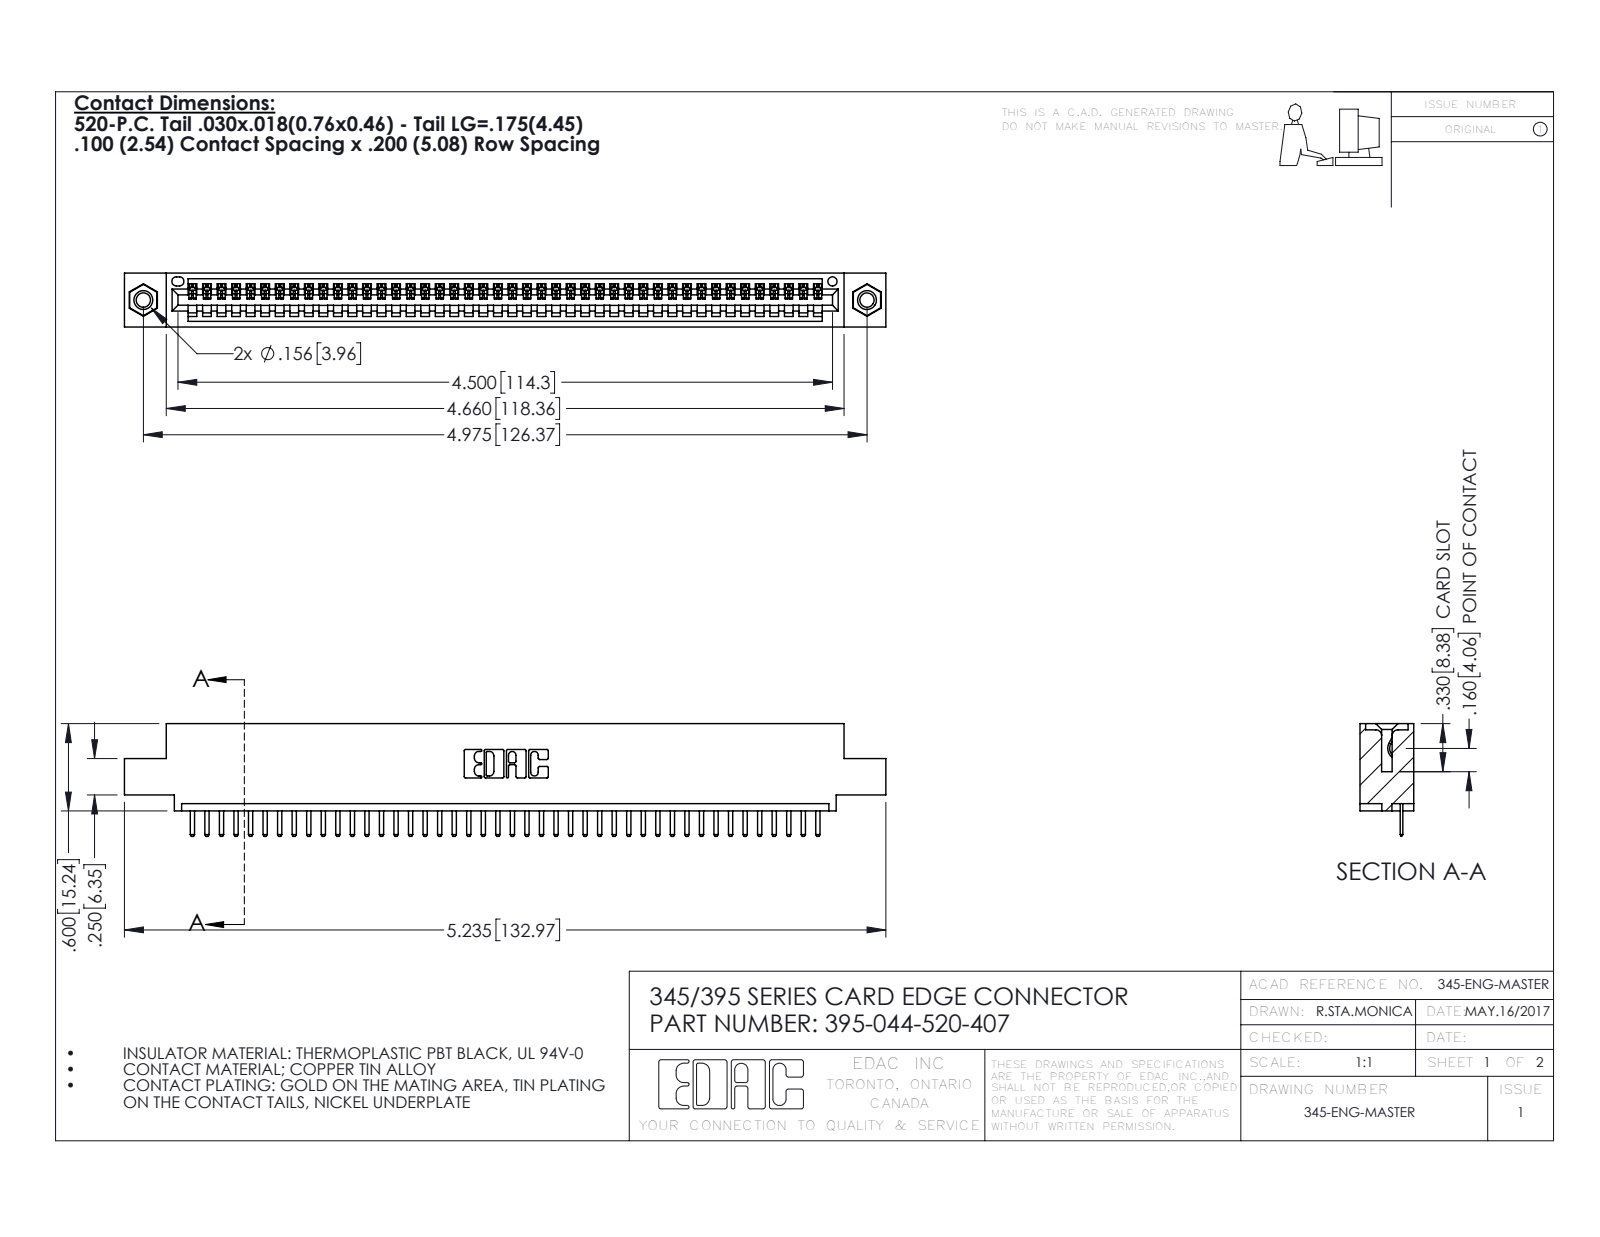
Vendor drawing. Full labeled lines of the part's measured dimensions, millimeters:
Part name (STEP PRODUCT): 345-292-001_345-293-120; 345 Part_0.110 Offset - 0.156 Dia-TI; 395-044-520-407; 345-250-001_345-250-005-103
STEP written by: SolidWorks 2016 (CONFIG_CONTROL_DESIGN)
Units: millimetres
Bodies: 47 solids, 2918 faces (1964 planar, 938 cylindrical, 16 other)
Overall size (bounding box): 133 × 19.7 × 9.4
Volume: 12 400 mm³ · Surface area: 16 250 mm²
Round holes (diameter × count): ⌀2.5 ×2, ⌀3.2 ×2, ⌀4 ×2, ⌀1.6 ×1
Round bosses / shafts (diameter × count): ⌀3.9 ×2
Partial cylindrical surfaces — rounded edges, fillets, slot ends (radius × count): R0.3 ×90, R0.2 ×88, R0.3 ×22, R0.2 ×6, R0.8 ×6, R0.7 ×3, R0.8 ×2, R1 ×2
Main face-to-face distances: 1.8, 7.6, 9.4, 5.1, 2.5, 6.9, 0.6, 5.7, 1.8, 3.8
Hole centre spacings: 6.9, 120.4, 126.4
